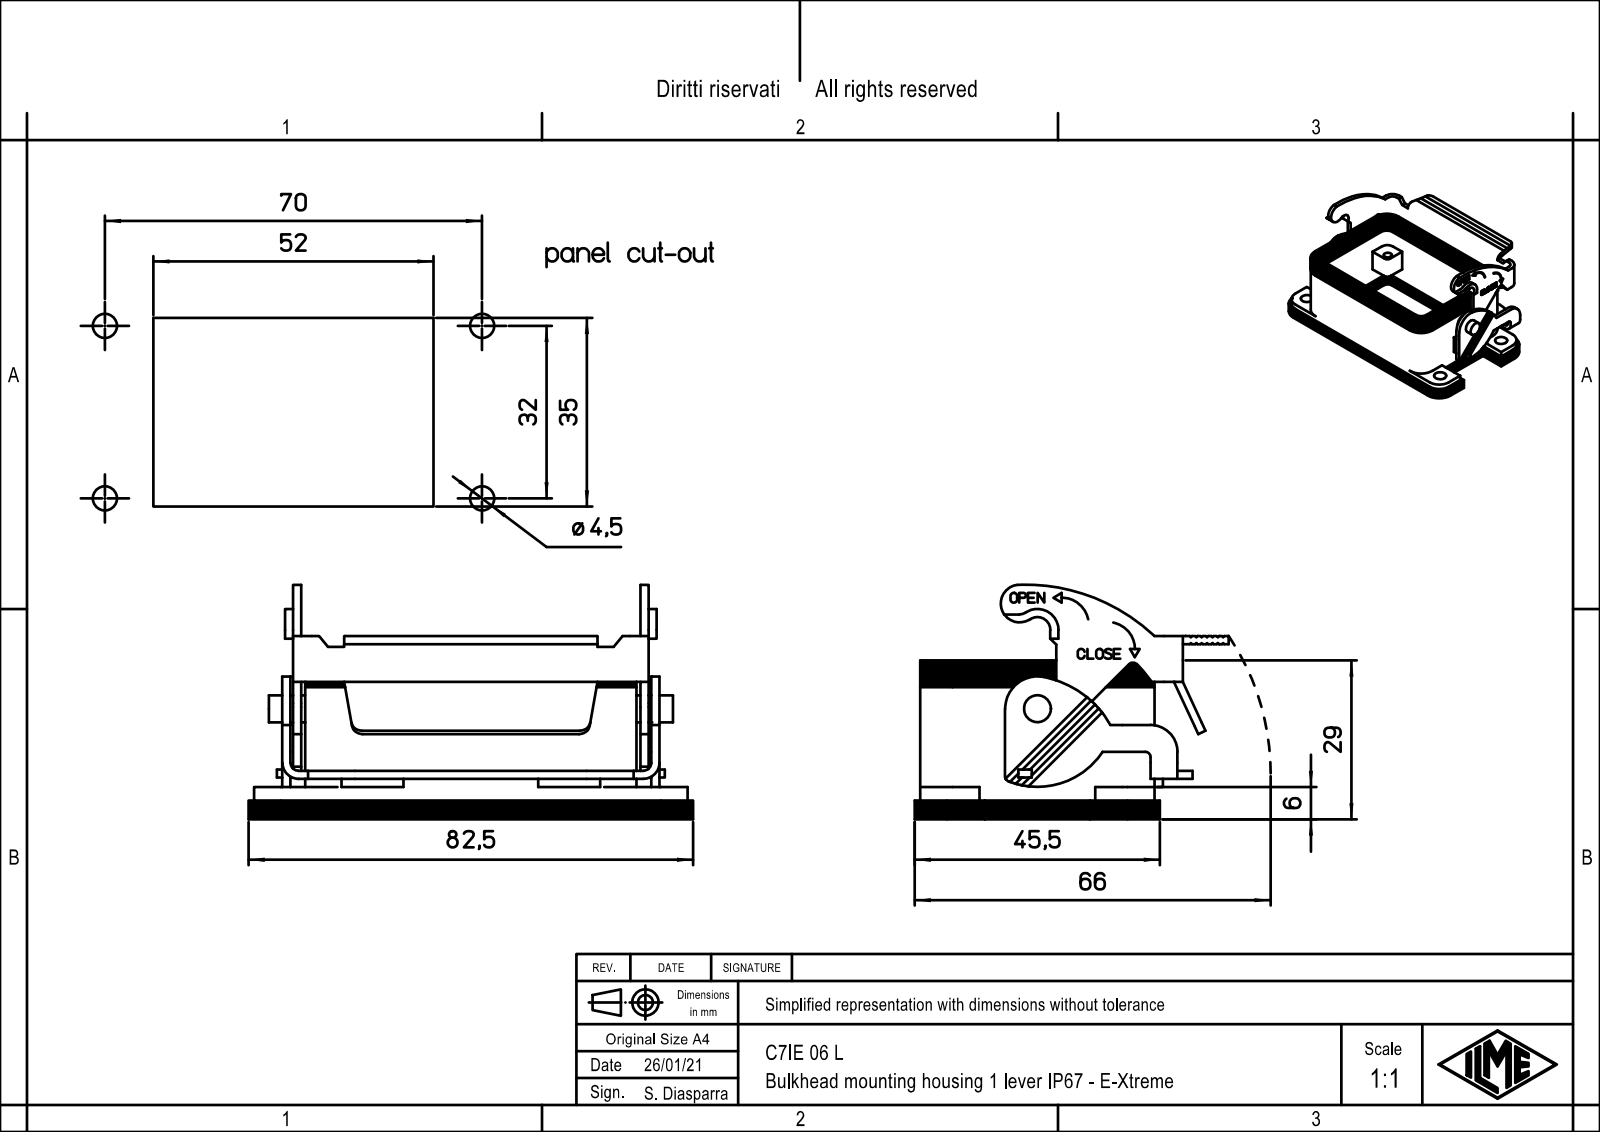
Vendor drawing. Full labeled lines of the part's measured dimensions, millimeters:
Part name (STEP PRODUCT): C7IE_06_L
STEP written by: Creo Elements/Direct Modeling 20.1B 02-Apr-2019 (C) Parametric Technology GmbH (AUTOMOTIVE_DESIGN)
Units: millimetres
Bodies: 1 solid, 413 faces (296 planar, 117 cylindrical, 0 other)
Overall size (bounding box): 82.5 × 58.25 × 43.5
Volume: 28 849 mm³ · Surface area: 24 197 mm²
Round holes (diameter × count): ⌀2.46 ×4, ⌀3 ×4, ⌀4.5 ×4
Round bosses / shafts (diameter × count): ⌀5 ×1
Partial cylindrical surfaces — rounded edges, fillets, slot ends (radius × count): R2 ×13, R3 ×10, R6 ×9, R1 ×6, R1.5 ×6, R5 ×5, R6.1 ×4, R3.5 ×3
Main face-to-face distances: 1.5, 3, 40.5, 3.5, 4, 0.5, 2, 66.5, 6, 62.25
Hole centre spacings: 13.24, 32.24, 57.05, 64.18, 27, 32, 44, 51.62
